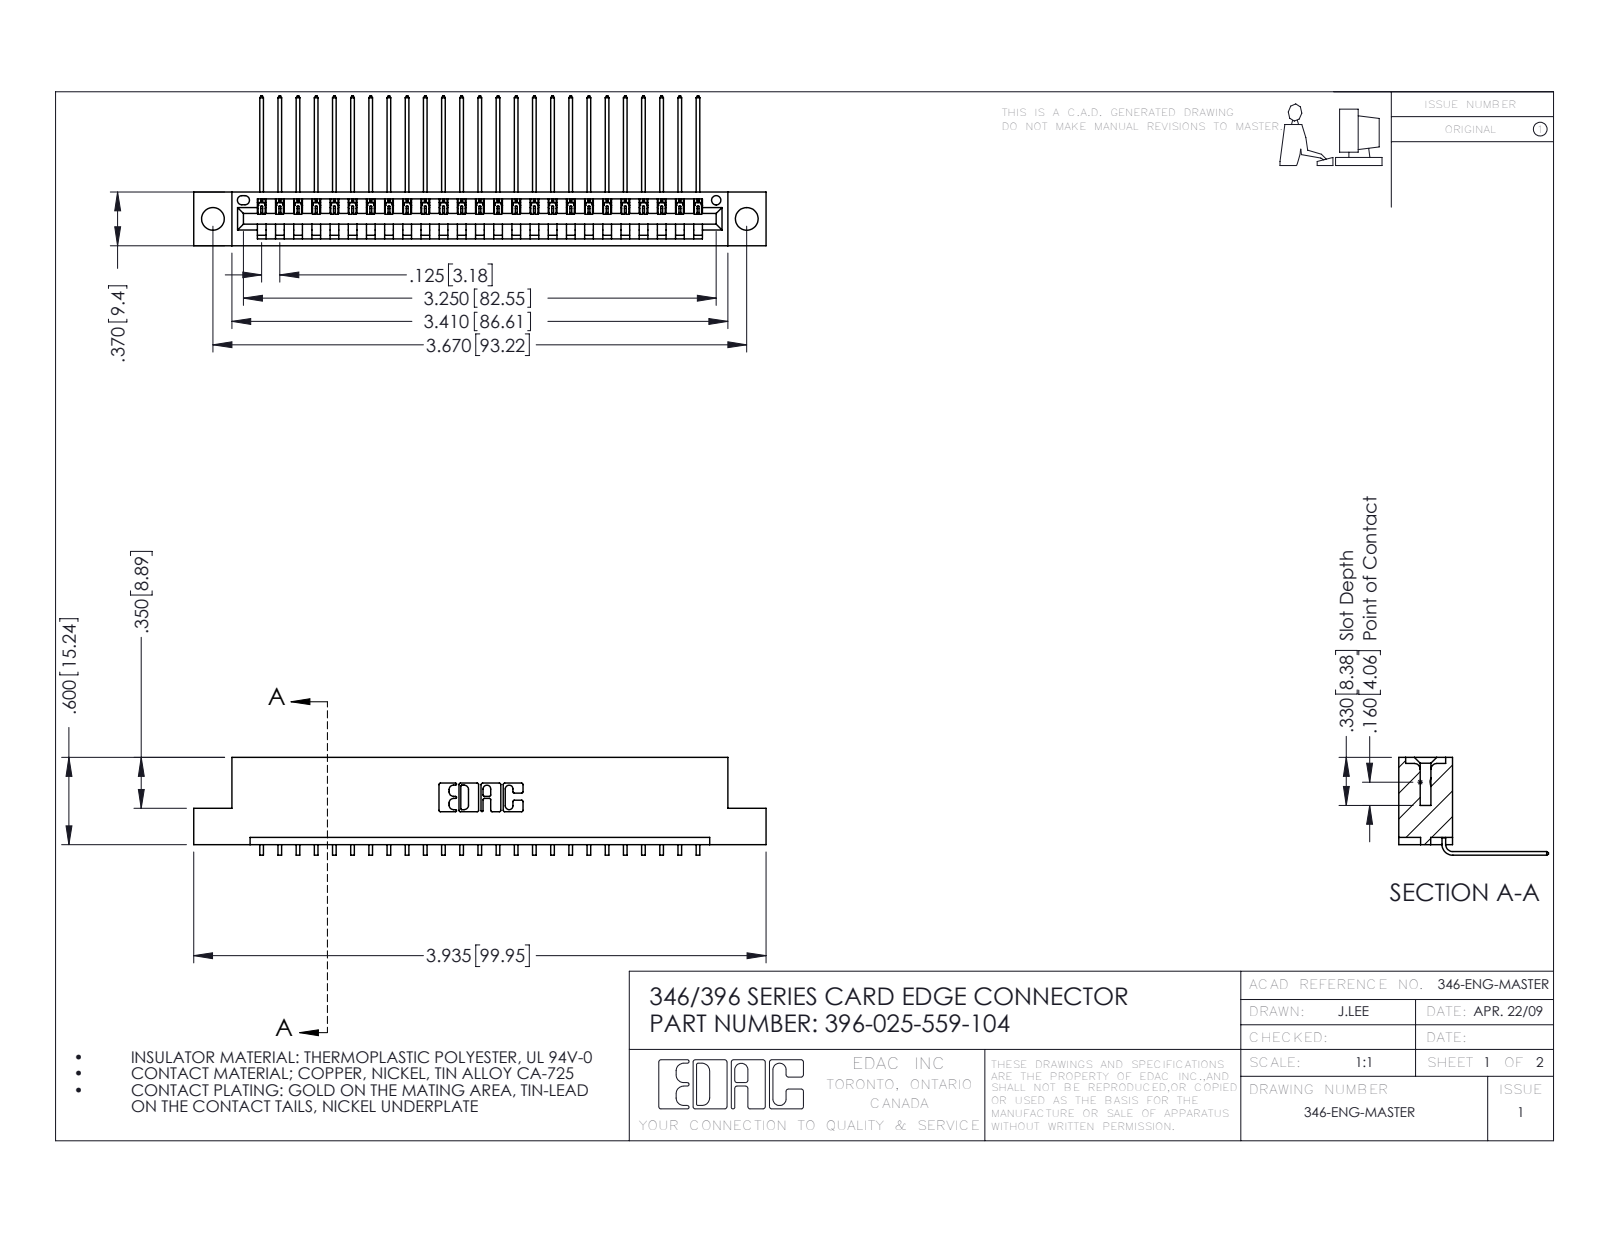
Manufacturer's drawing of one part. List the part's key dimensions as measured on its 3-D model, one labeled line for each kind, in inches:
Part name (STEP PRODUCT): 396-025-559-104; 345-292-001_558 559 Tail - 1; 346 Part_Flush Mounting Lugs - 0.156 Dia-TH
STEP written by: SolidWorks 2016 (CONFIG_CONTROL_DESIGN)
Units: inches
Bodies: 26 solids, 1622 faces (1126 planar, 496 cylindrical, 0 other)
Overall size (bounding box): 3.935 × 1.03 × 0.673
Volume: 0.576 in³ · Surface area: 18.48 in²
Round holes (diameter × count): ⌀0.156 ×2, ⌀0.064 ×1
Partial cylindrical surfaces — rounded edges, fillets, slot ends (radius × count): R0.006 ×50, R0.01 ×22, R0.007 ×6, R0.031 ×6, R0.026 ×3, R0.031 ×2, R0.04 ×2, R0.014 ×1
Main face-to-face distances: 0.048, 0.322, 0.37, 0.25, 0.072, 0.025, 0.298, 0.148, 0.222, 0.1
Hole centre spacings: 0.246, 3.462, 3.67
